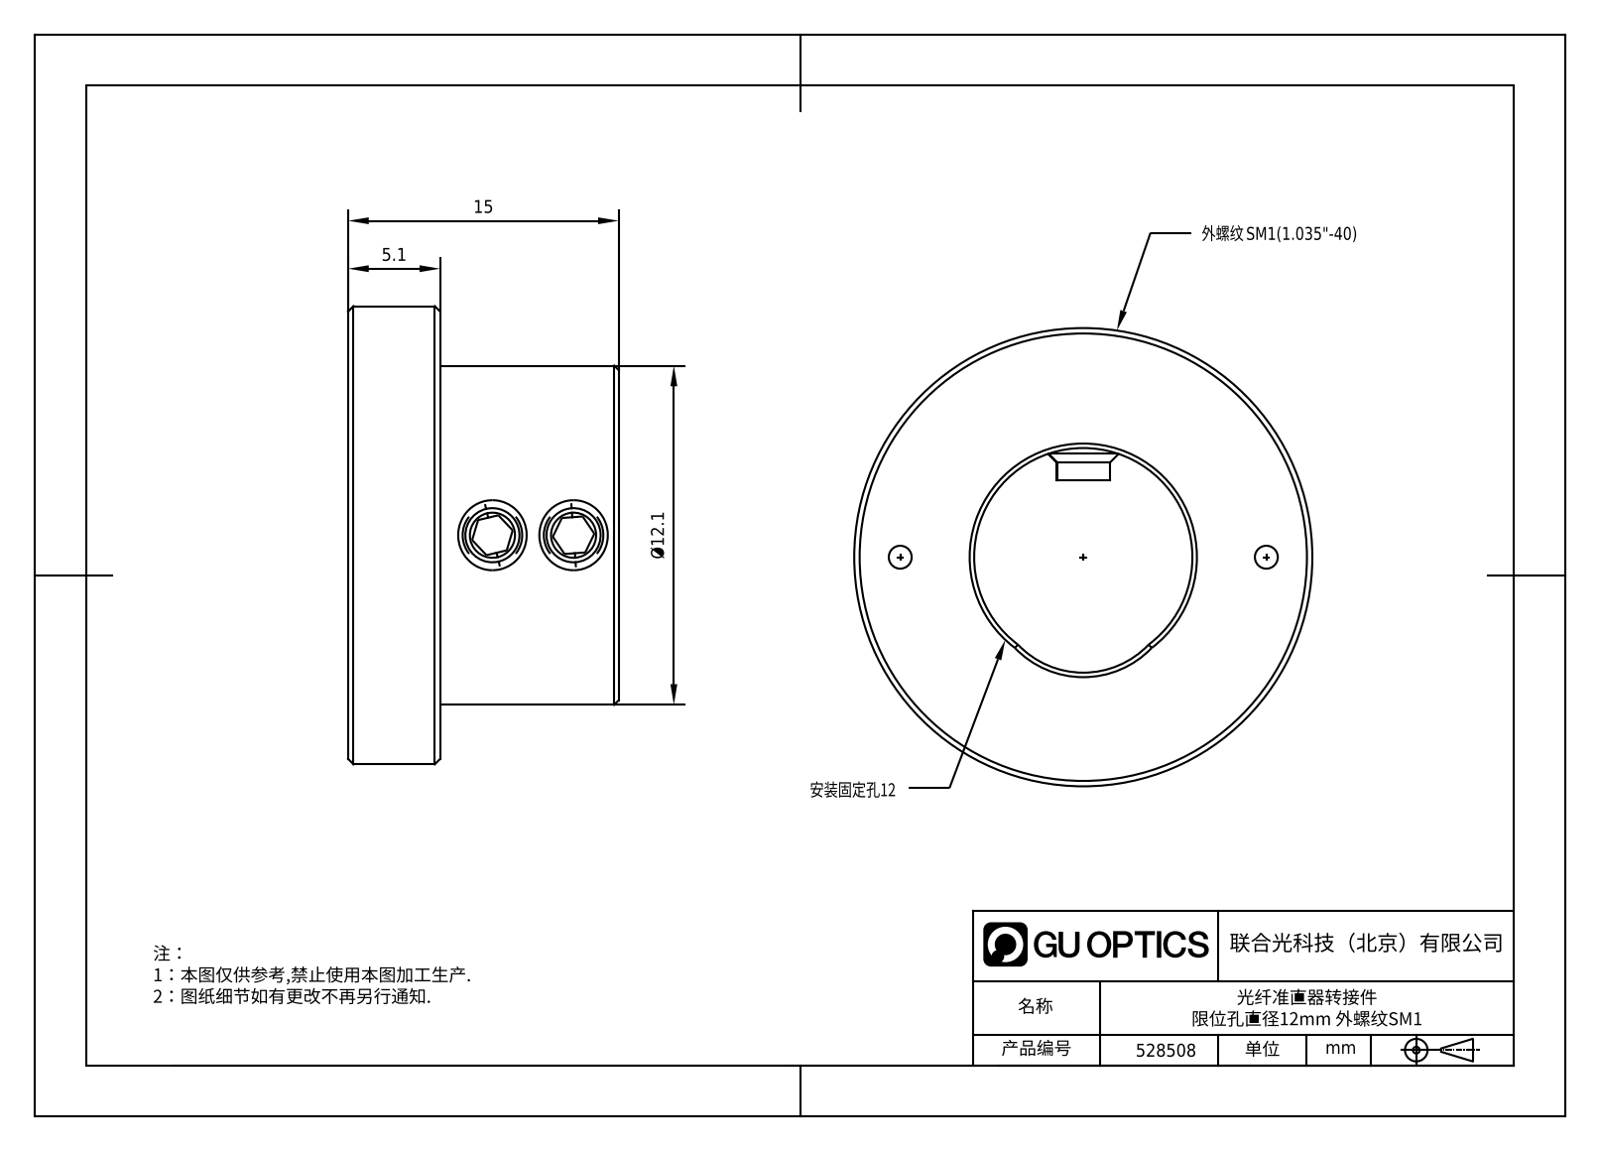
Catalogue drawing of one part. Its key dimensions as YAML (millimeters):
part_name: "1.6.5.9_ZSG-1W12N"
step_written_by: "SolidWorks 2021 (CONFIG_CONTROL_DESIGN)"
units: millimeters
bodies: {solids: 3, faces: 83, planar: 25, cylindrical: 28, other: 30}
overall_size: [25.4, 25.4, 15]
volume: 3593
surface_area: 2505
round_holes:
  - {diameter: 1.27, count: 4}
  - {diameter: 3.3, count: 2}
  - {diameter: 12.1, count: 1}
round_bosses_or_shafts:
  - {diameter: 4, count: 2}
  - {diameter: 3, count: 2}
  - {diameter: 25.4, count: 1}
  - {diameter: 18.8, count: 1}
partial_cylinders:
  - {radius: 5, count: 1}
face_to_face_distances: [5.1, 15, 9.9, 1, 4, 3, 2, 1.27, 3.83, 5]
hole_center_spacings: [10.15, 14.35, 20.3, 4.5]
